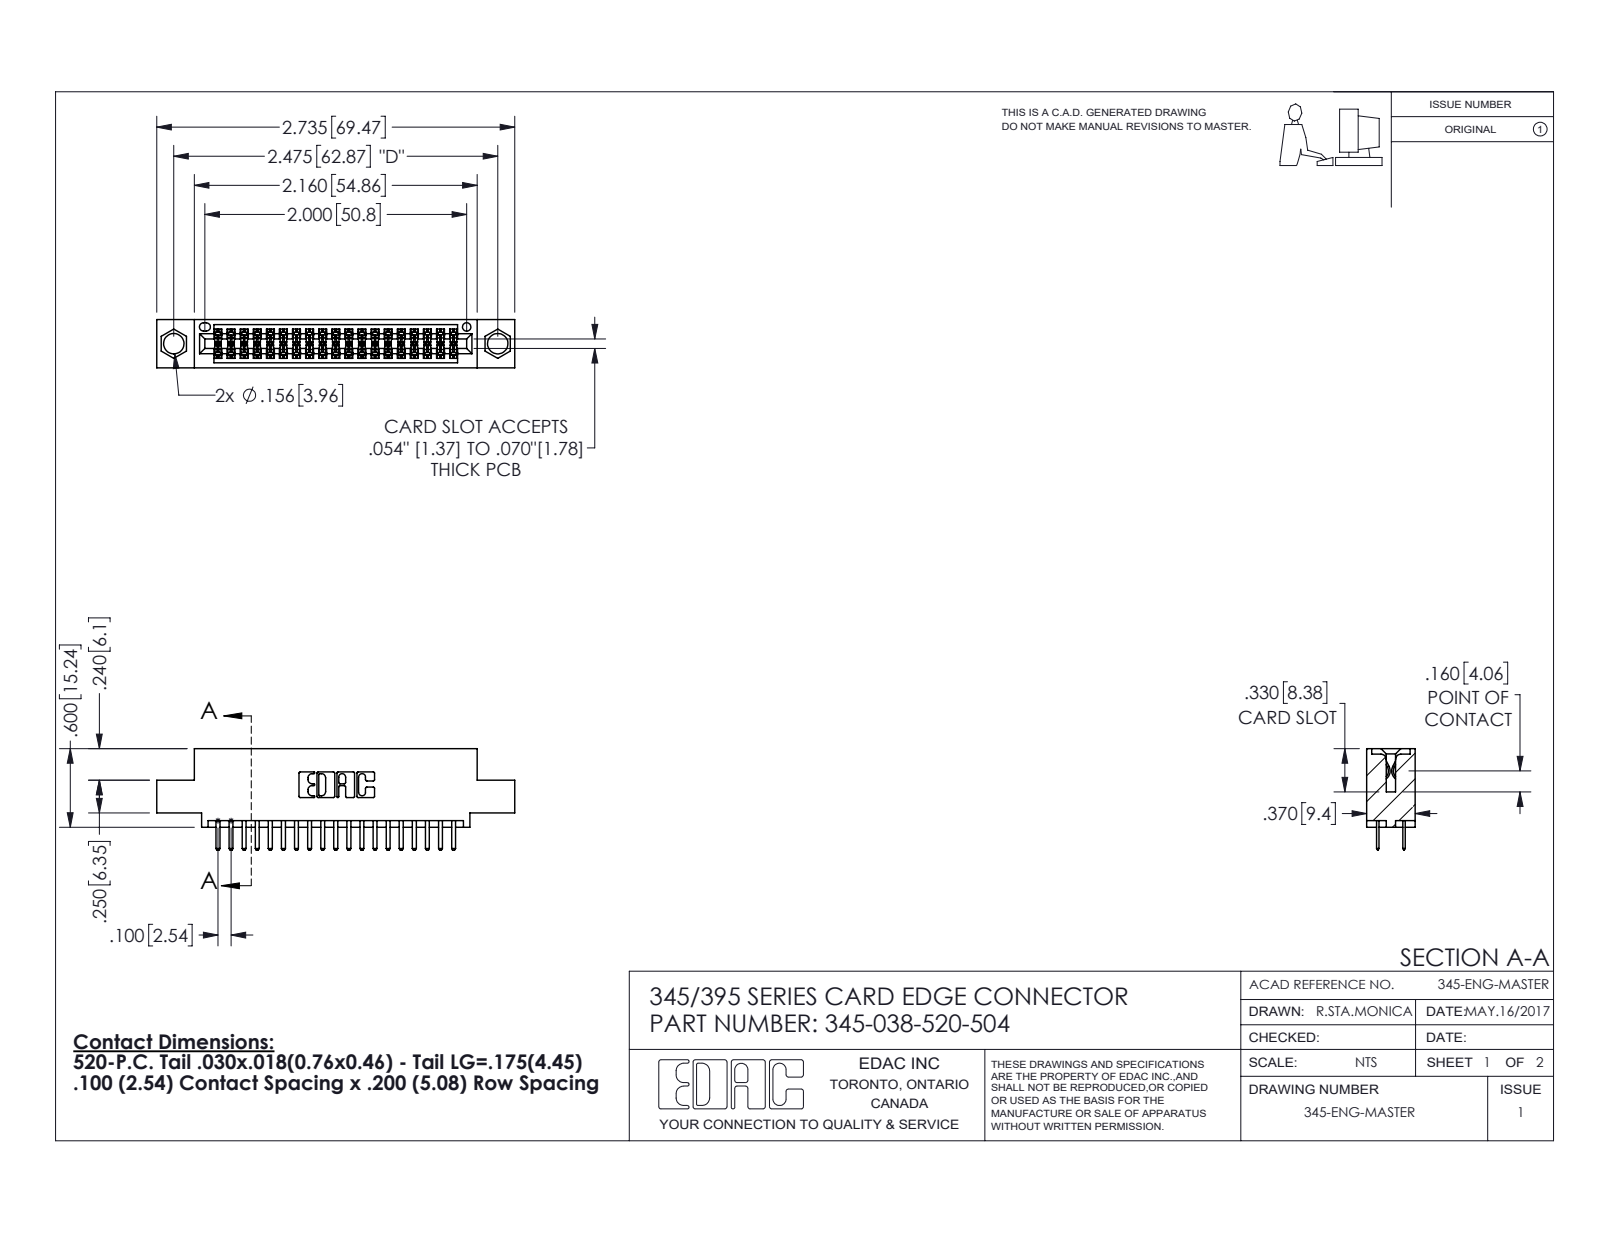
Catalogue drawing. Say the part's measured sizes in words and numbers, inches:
The part is named "345-292-001_345-293-120; 345-038-520-504; 345 Part_0.110 Offset - 0.156 Dia-TI". Its 3-D file was written by "SolidWorks 2020 (CONFIG_CONTROL_DESIGN)". It is 39 solids with 2196 faces: 1428 planar, 768 cylindrical and 0 other. Overall it measures 2.735 by 0.775 by 0.37 inches. Its volume is 0.387 cubic inches and its surface area 13.69 square inches. Round holes: 2 of diameter 0.156, 1 of diameter 0.064. Partial cylindrical surfaces (rounded edges, fillets, slot ends): 57 of radius 0.006, 42 of radius 0.01, 22 of radius 0.01, 6 of radius 0.007, 6 of radius 0.031, 3 of radius 0.026, 2 of radius 0.014, 2 of radius 0.019. The main face-to-face distances are 0.298, 0.072, 0.2, 0.37, 0.098, 0.272, 0.025, 0.225, 0.022, 0.072. The hole center spacings are 0.27, 2.241, 2.475.
